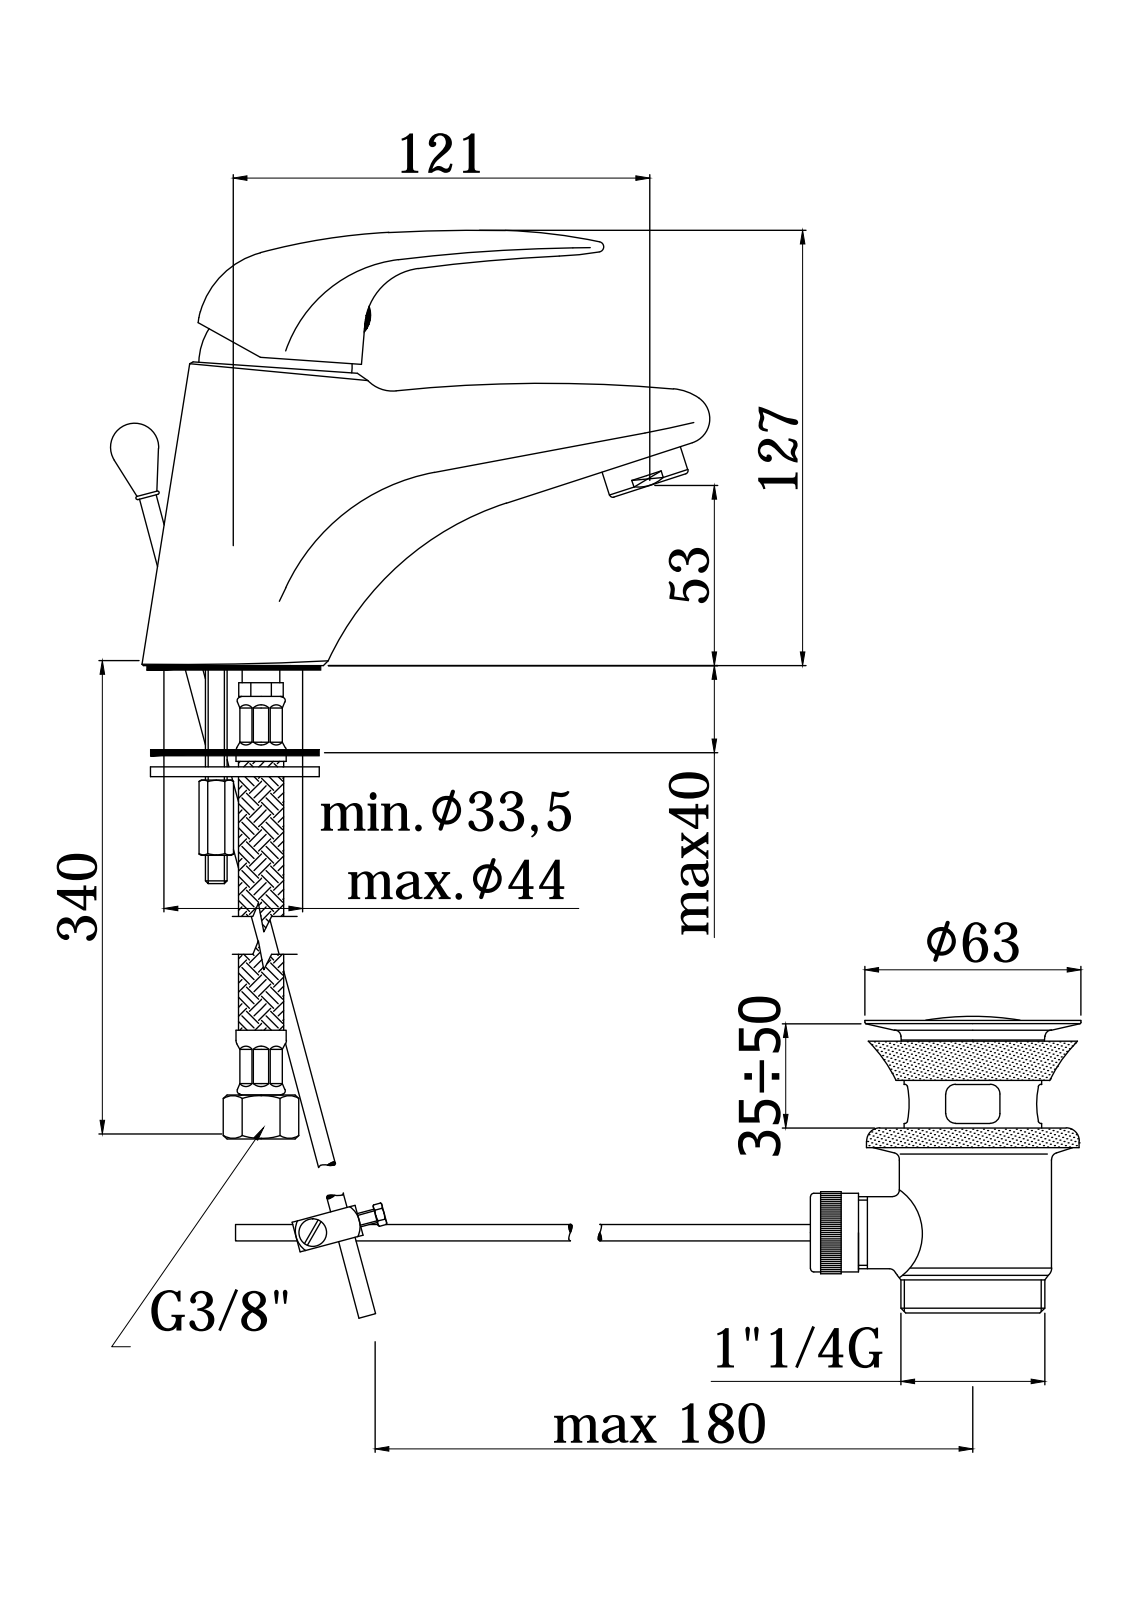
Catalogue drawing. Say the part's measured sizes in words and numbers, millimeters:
The part is named "DU075CR". Its 3-D file was written by "CREO PARAMETRIC BY PTC INC, 2020044 (CONFIG_CONTROL_DESIGN)". It is 4 solids with 2619 faces: 1949 planar, 356 cylindrical and 314 other. Overall it measures 173.86 by 130.19 by 53.5 millimeters. Its volume is 323 823 cubic millimeters and its surface area 85 235 square millimeters. Round holes: 4 of diameter 8, 3 of diameter 11, 2 of diameter 5.25, 2 of diameter 5.5, 2 of diameter 7, 2 of diameter 9, 2 of diameter 12, 2 of diameter 21, 1 of diameter 3.3, 1 of diameter 4, 1 of diameter 4.5, 1 of diameter 5. Round bosses or shafts: 2 of diameter 15.9, 2 of diameter 9.4, 2 of diameter 5, 1 of diameter 44.5, 1 of diameter 39.5, 1 of diameter 39.2, 1 of diameter 38.8, 1 of diameter 34.8. Partial cylindrical surfaces (rounded edges, fillets, slot ends): 53 of radius 0.5, 24 of radius 0.2, 6 of radius 1.5, 4 of radius 0.3, 2 of radius 5.5, 2 of radius 7.5, 2 of radius 15, 2 of radius 24. The main face-to-face distances are 1, 0.5, 4, 3.5, 37.41, 5, 1.3, 10, 1.5, 50.82. The hole center spacings are 9.9, 8.61, 6, 2, 8.6, 10.97, 12.08, 13.04.
